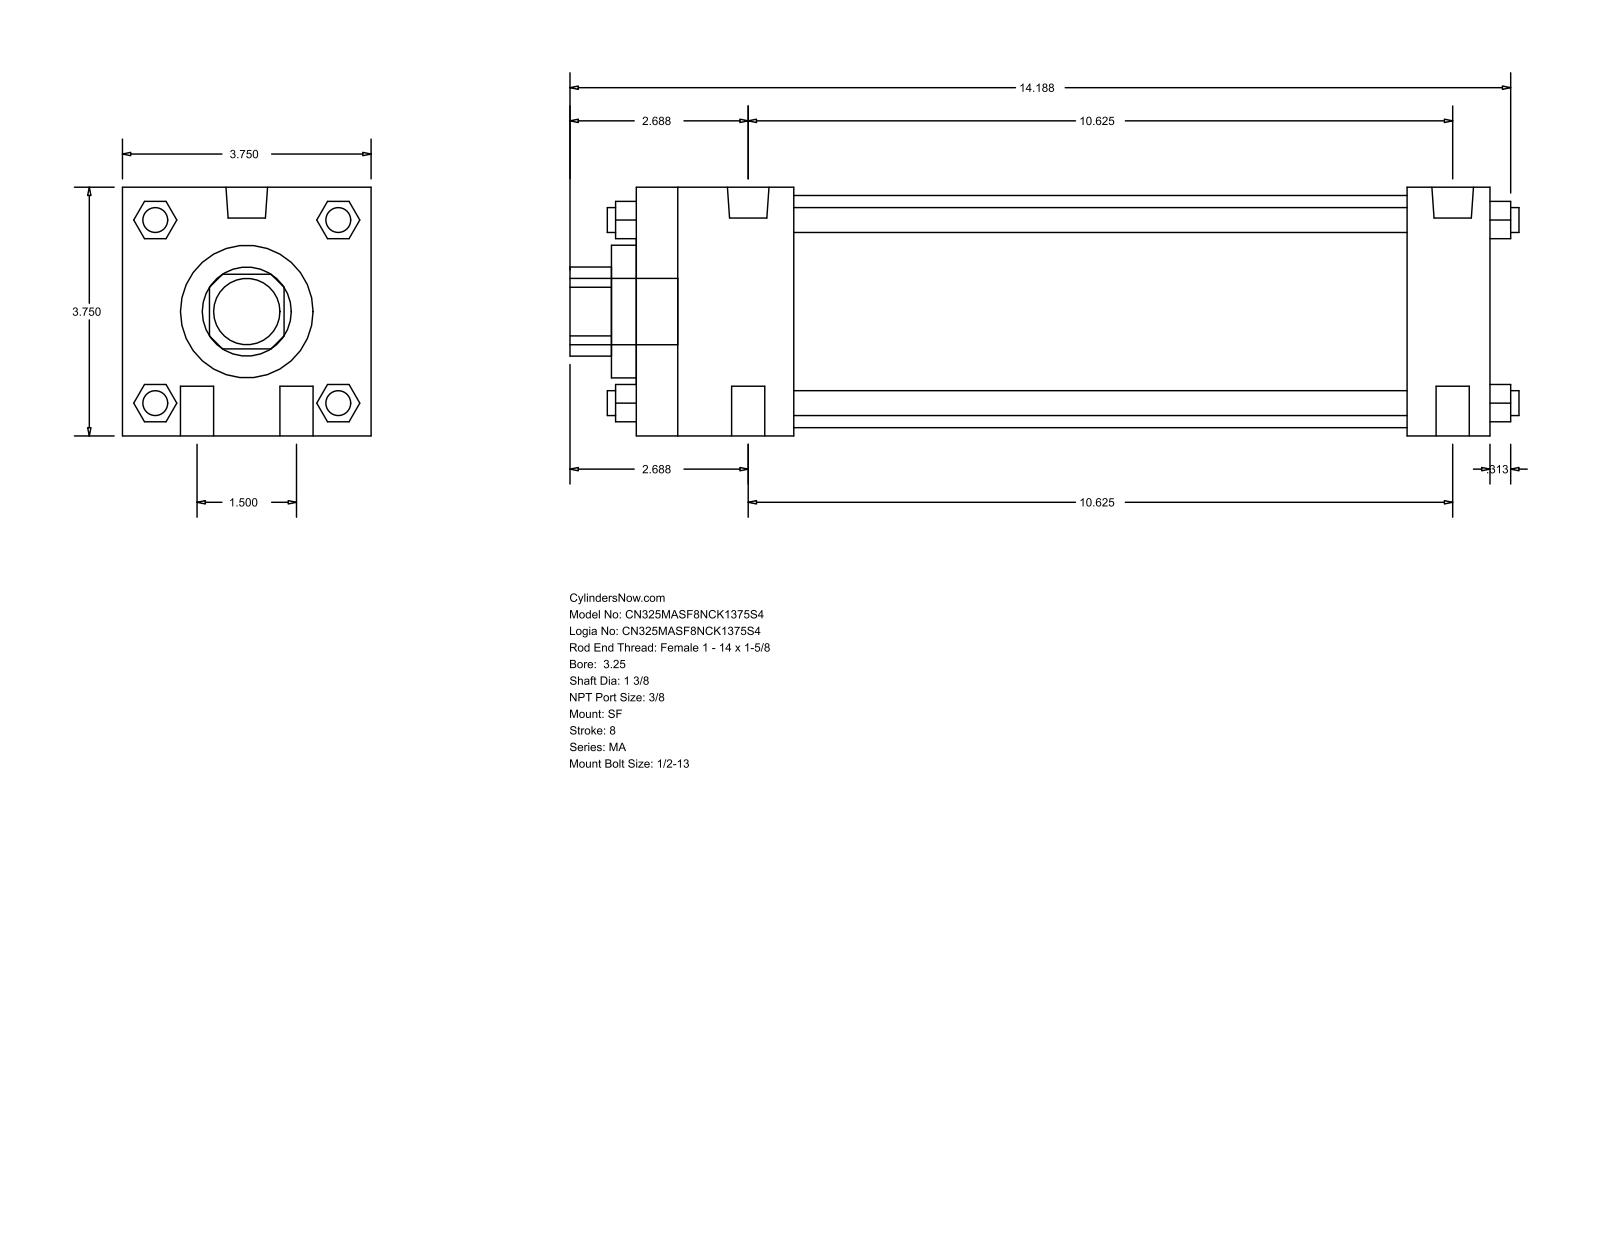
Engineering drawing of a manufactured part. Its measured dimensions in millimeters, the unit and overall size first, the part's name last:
Units: millimetres
Overall size (bounding box): 363.54 × 95.25 × 95.25
Round holes (diameter × count): ⌀34.92 ×1, ⌀50.8 ×1, ⌀88.9 ×1
Round bosses / shafts (diameter × count): ⌀12.7 ×4, ⌀9.53 ×4, ⌀15.93 ×2, ⌀11.11 ×2, ⌀25.4 ×1
Partial cylindrical surfaces — rounded edges, fillets, slot ends (radius × count): R17.06 ×1
Main face-to-face distances: 95.24, 327.03, 295.28, 31.75, 60.32, 234.96, 266.71, 9.52, 69.84, 304.8
Bodies: 0 solids, 124 faces (94 planar, 30 cylindrical, 0 other)
Part name (STEP PRODUCT): MA_SF__0325_1.375
STEP written by: GSSL Pune (CONFIG_CONTROL_DESIGN)
